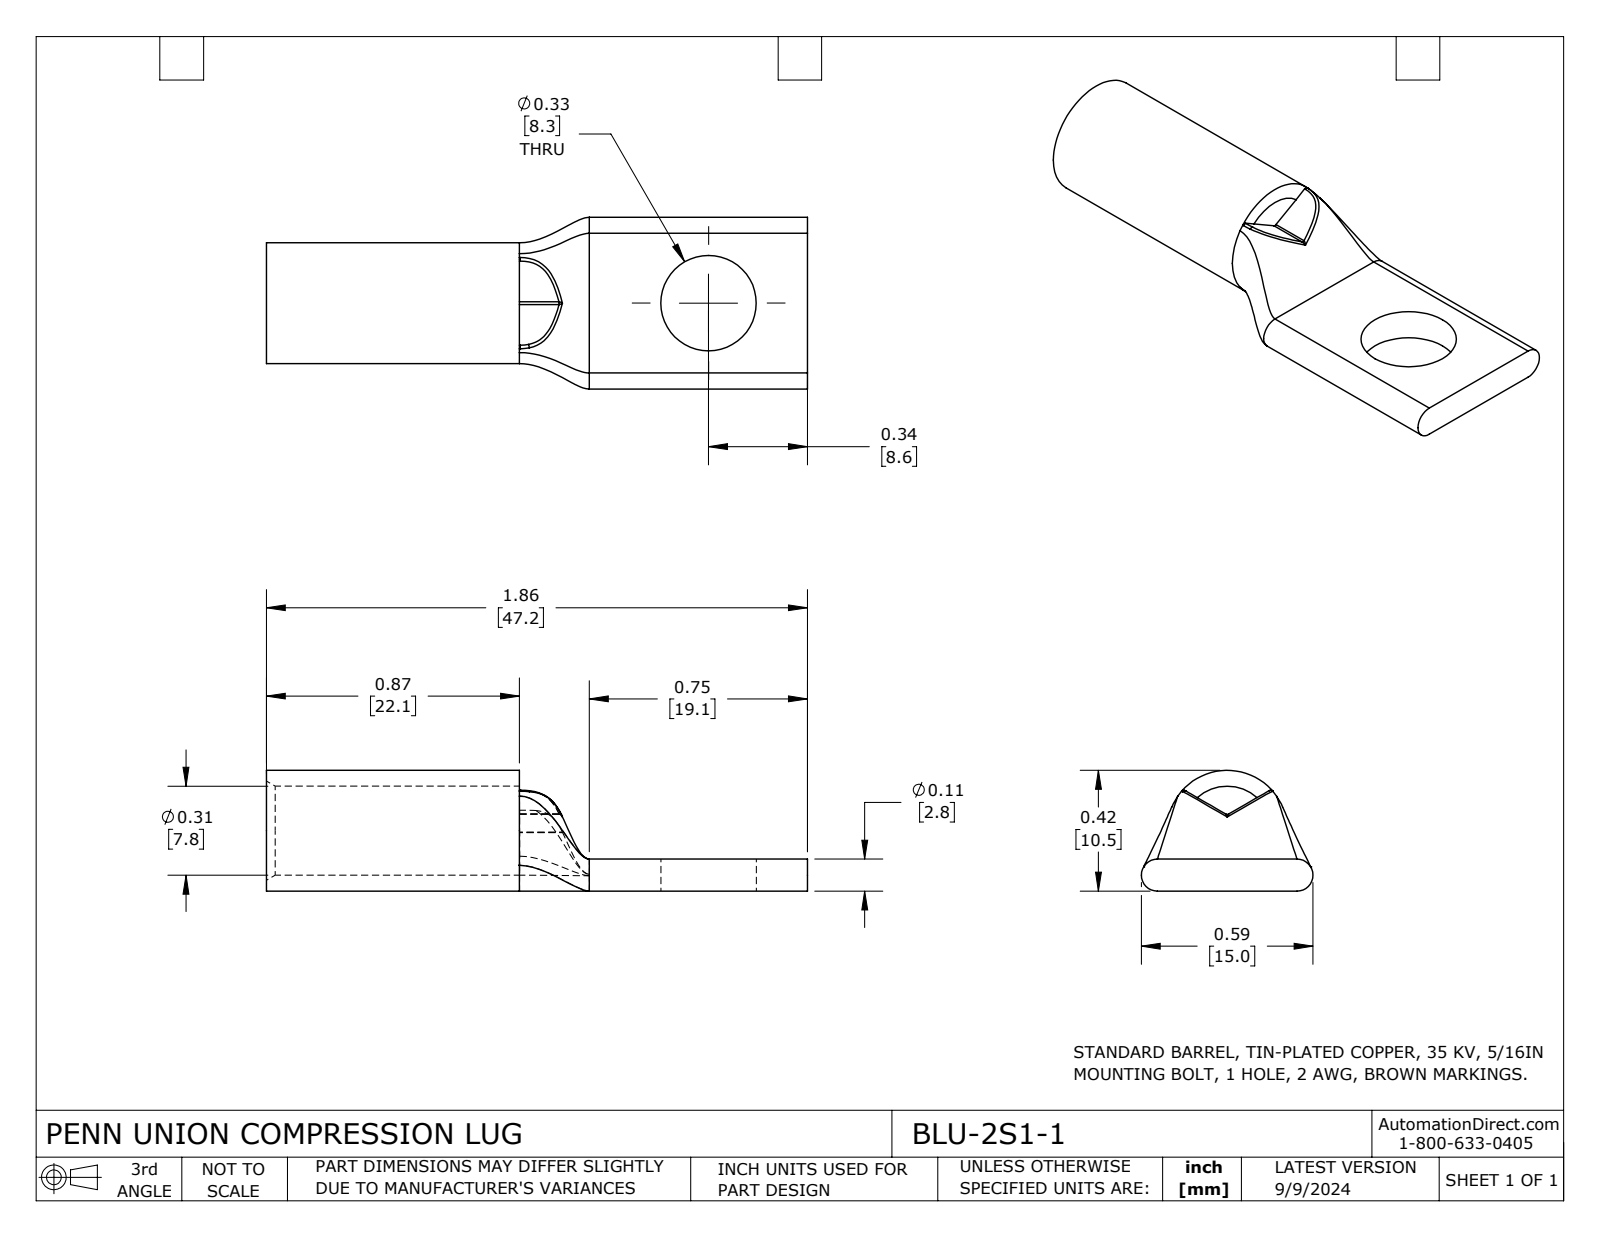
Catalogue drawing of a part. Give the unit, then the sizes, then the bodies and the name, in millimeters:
Units: millimetres
Overall size (bounding box): 47.2 × 15 × 10.5
Round holes (diameter × count): ⌀7.8 ×1, ⌀8.3 ×1
Round bosses / shafts (diameter × count): ⌀10.5 ×1
Partial cylindrical surfaces — rounded edges, fillets, slot ends (radius × count): R0.3 ×2, R1.4 ×2
Main face-to-face distances: 2.8, 47.2, 1.4, 22.1, 25.1, 28.2, 6.1, 19.1
Volume: 1 720 mm³ · Surface area: 2 374 mm²
Bodies: 1 solid, 38 faces (11 planar, 11 cylindrical, 16 other)
Part name (STEP PRODUCT): BLU-2S1-1
STEP written by: SolidWorks 2023 (CONFIG_CONTROL_DESIGN)
